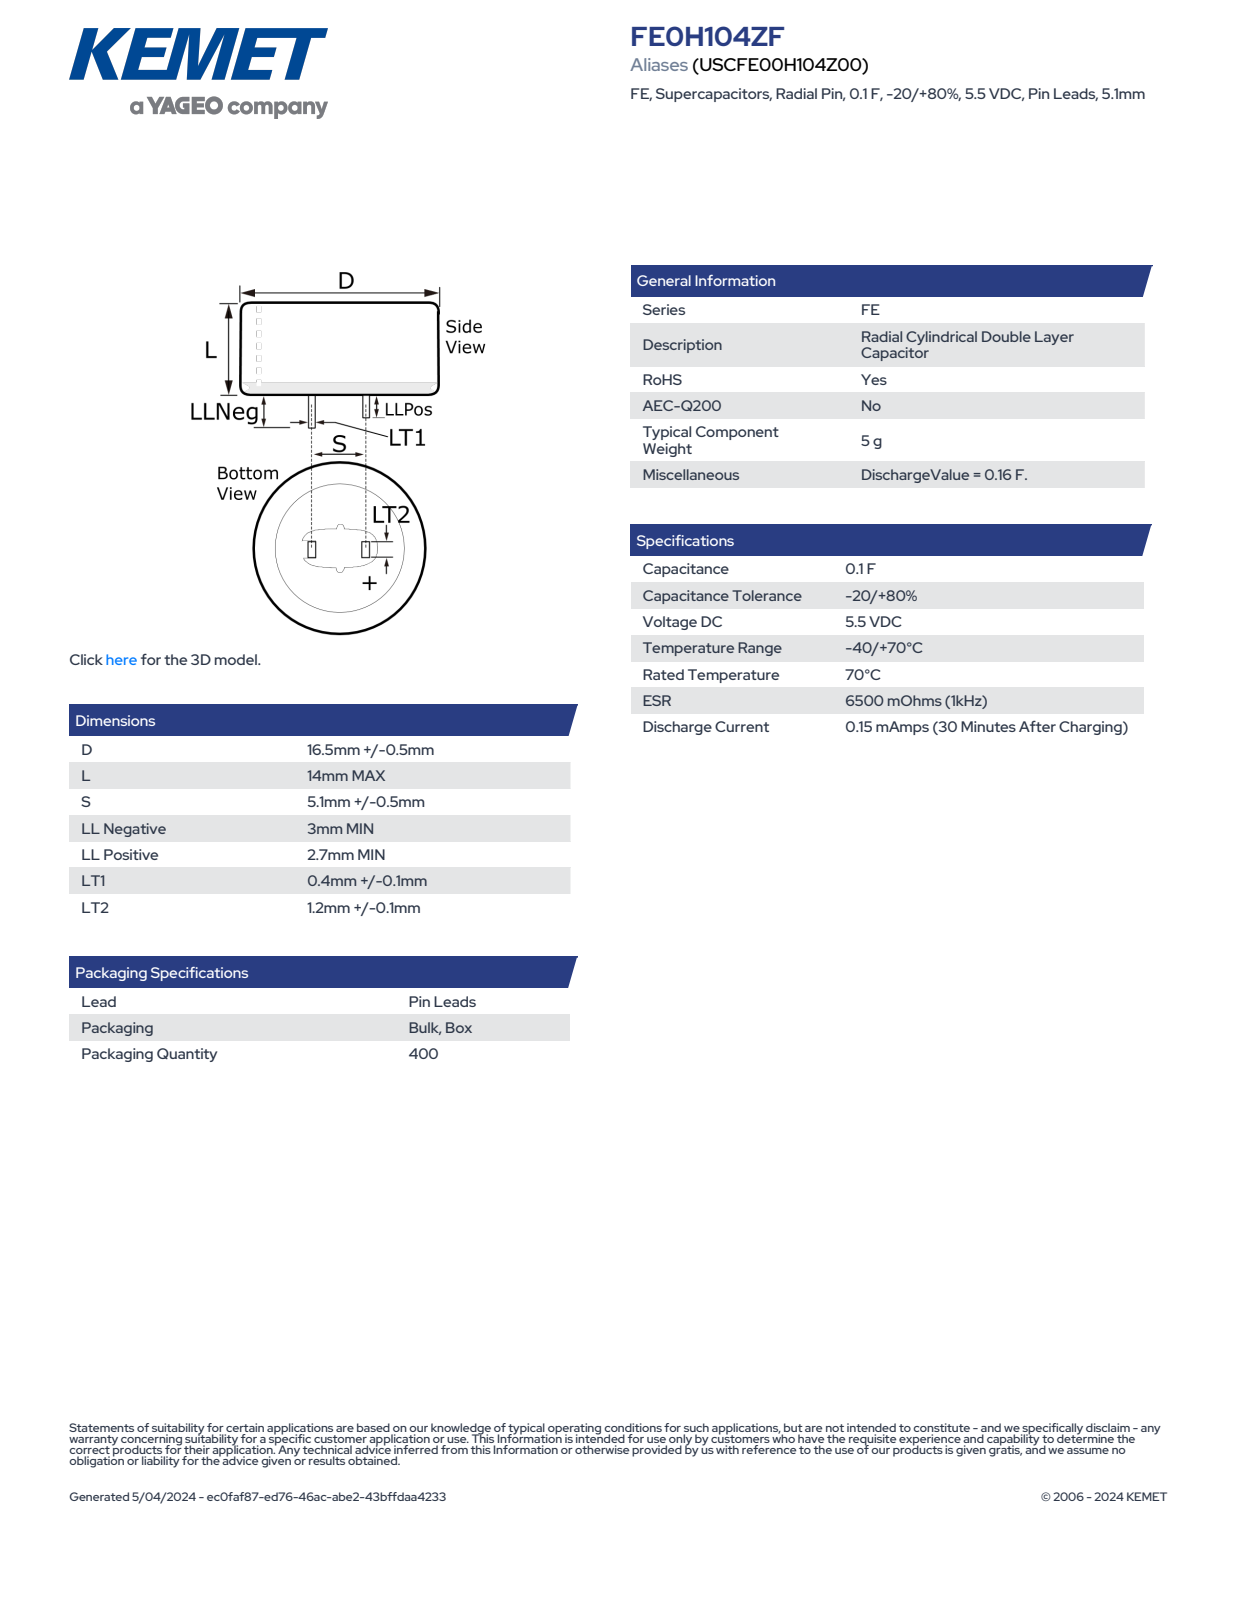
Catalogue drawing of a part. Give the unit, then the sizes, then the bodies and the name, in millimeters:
Units: millimetres
Overall size (bounding box): 17 × 17 × 17
Round bosses / shafts (diameter × count): ⌀17 ×1
Partial cylindrical surfaces — rounded edges, fillets, slot ends (radius × count): R8.51 ×1
Main face-to-face distances: 14, 0.5, 5.1, 5.6, 4.6, 1.3, 3, 17, 2.7, 16.7
Volume: 3 163 mm³ · Surface area: 1 181 mm²
Bodies: 1 solid, 78 faces (70 planar, 4 cylindrical, 4 other)
Part name (STEP PRODUCT): CDR_LPLLN_D17L14S5.1LLNEG3LLPOS2.7LT10.5LT21.3
STEP written by: SolidWorks 2014 (AUTOMOTIVE_DESIGN)
